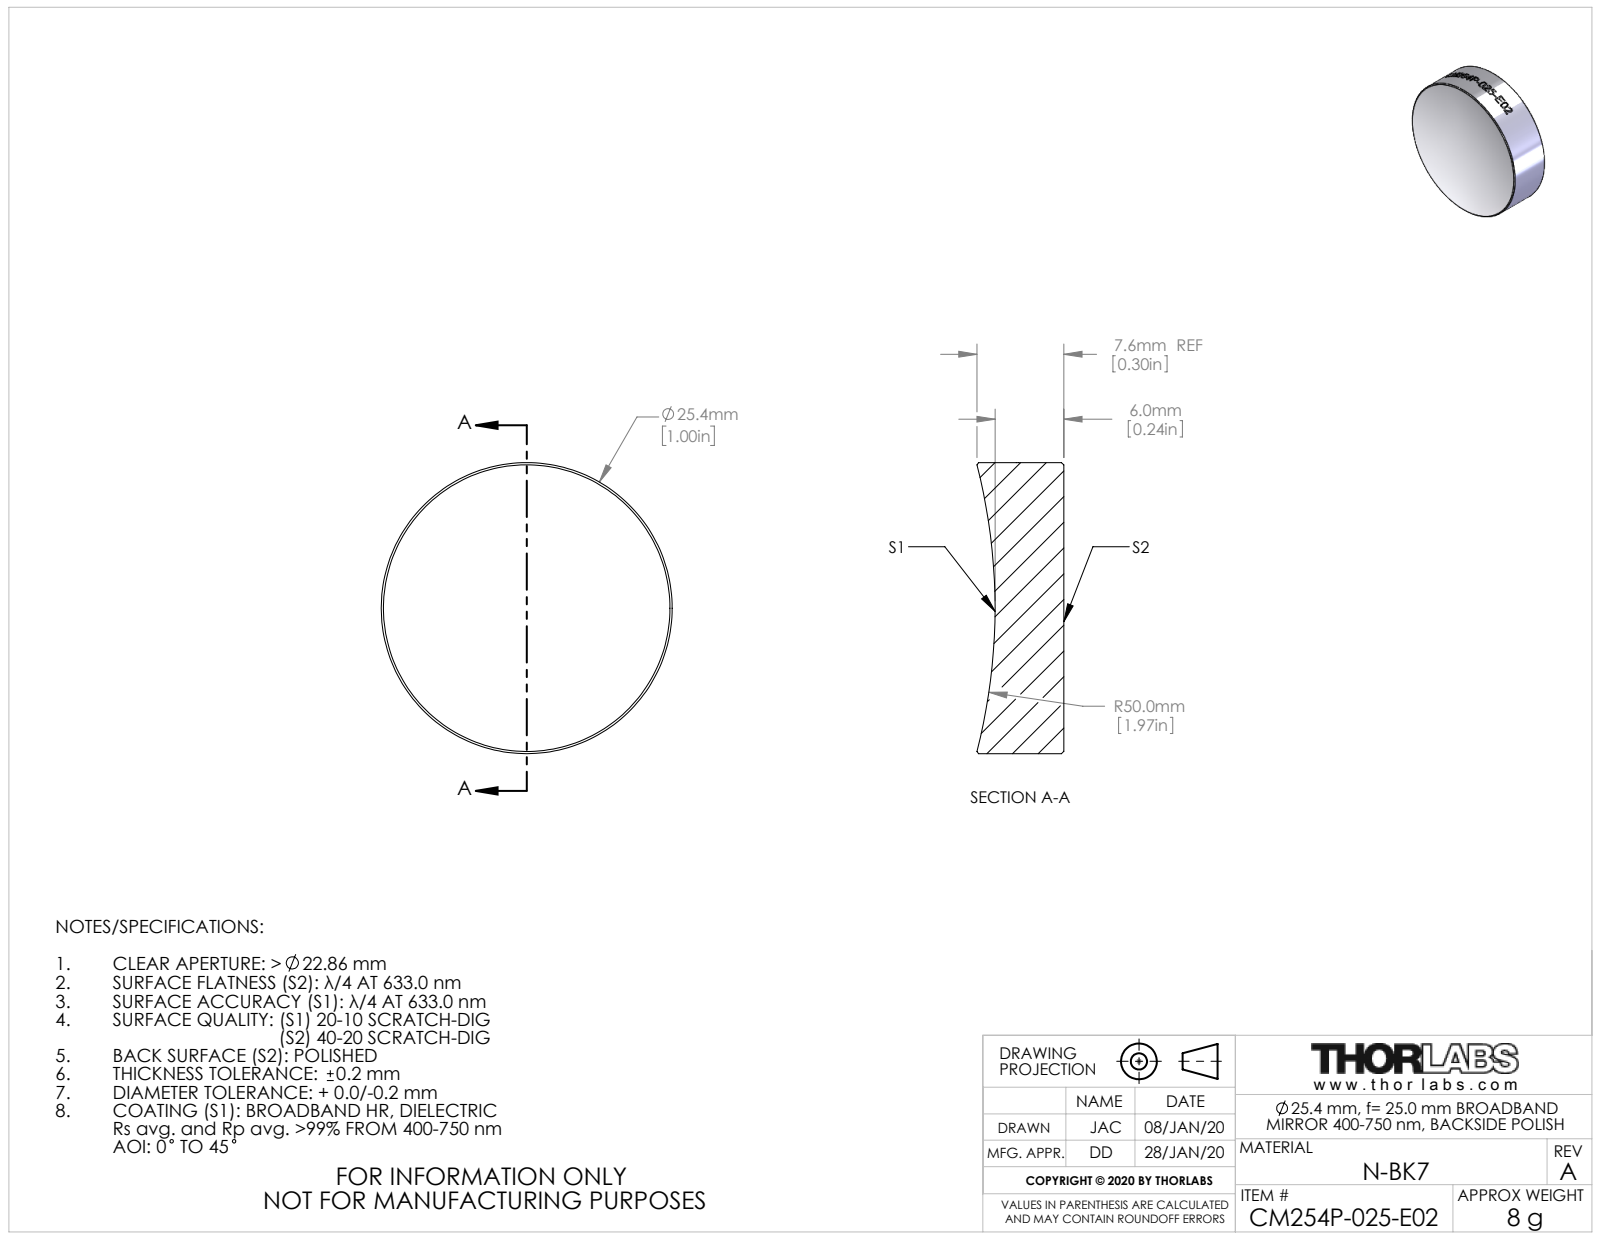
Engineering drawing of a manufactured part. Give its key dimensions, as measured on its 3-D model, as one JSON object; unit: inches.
{"part_name": "TTN201330-E0W", "step_written_by": "SolidWorks 2018 (CONFIG_CONTROL_DESIGN)", "units": "inches", "bodies": {"solids": 1, "faces": 27, "planar": 1, "cylindrical": 20, "other": 6}, "overall_size": [1, 1, 0.299], "volume_in3": 0.211, "surface_area_in2": 2.496, "round_bosses_or_shafts": [[1, 1]]}
